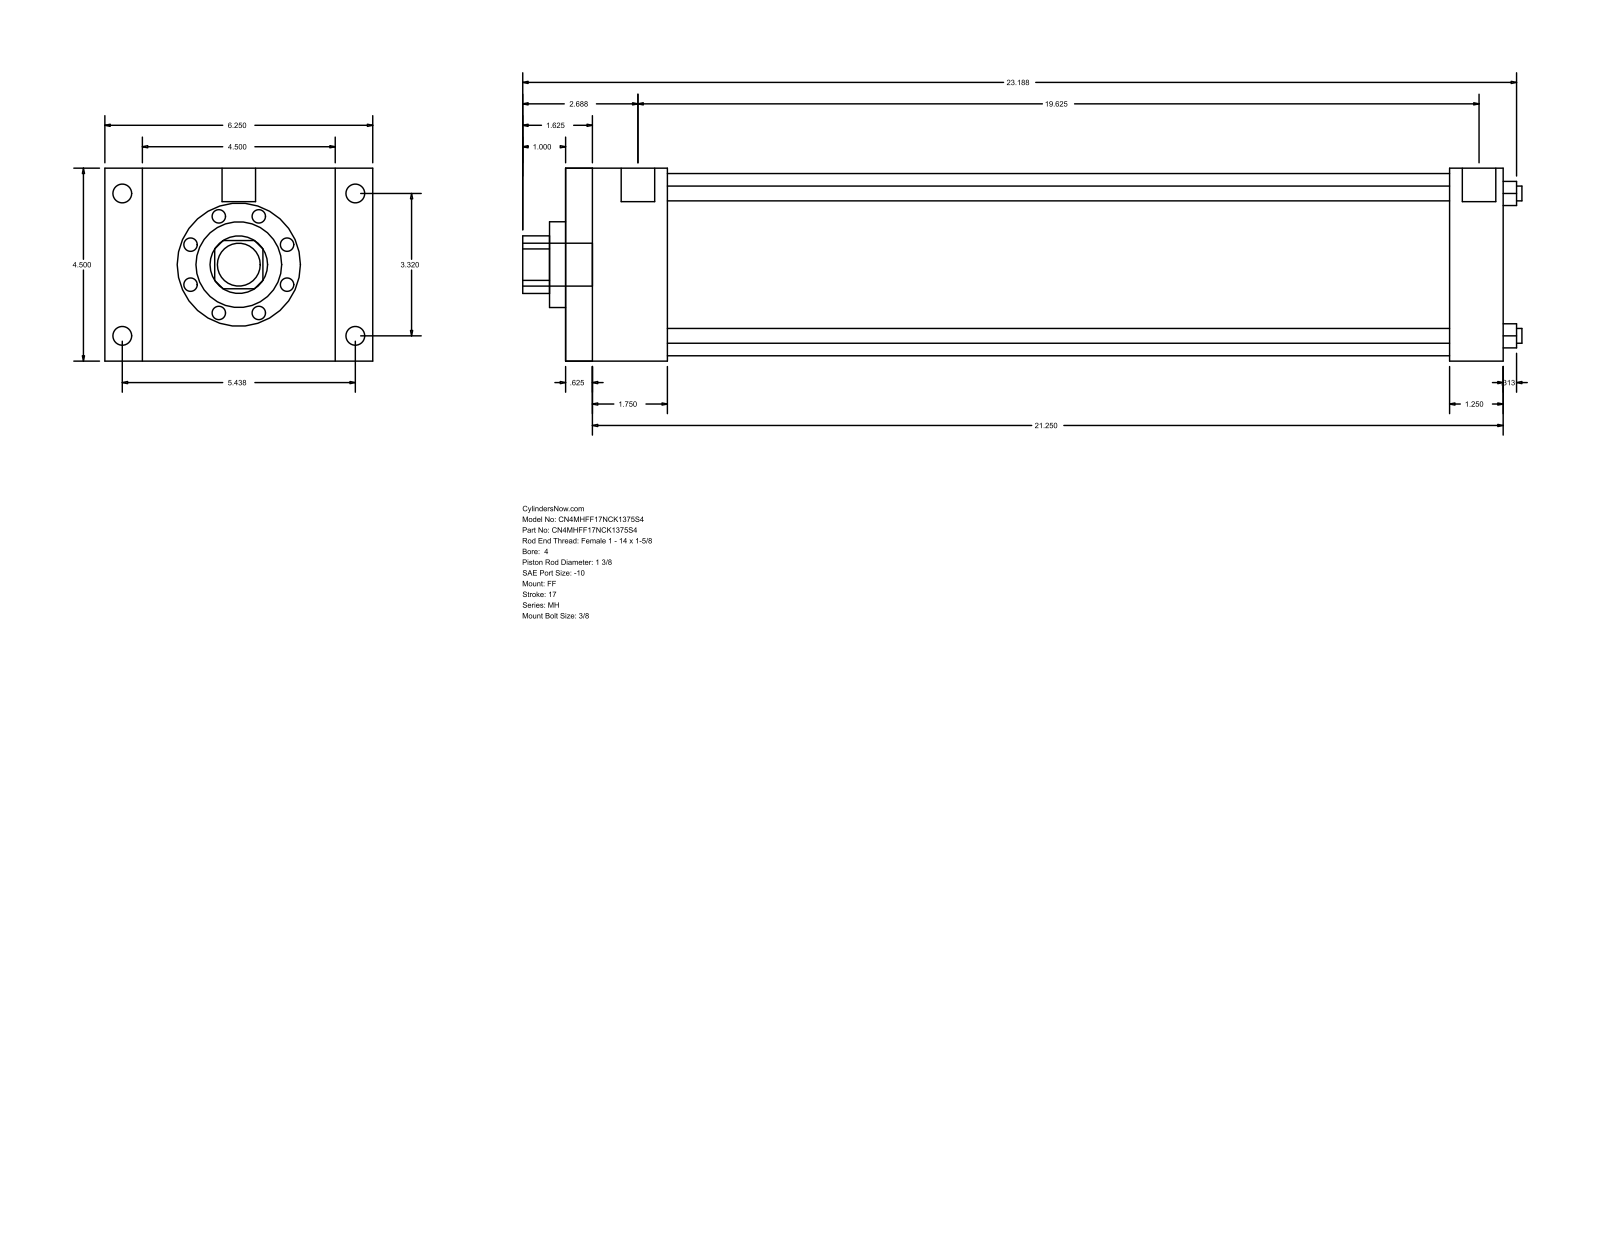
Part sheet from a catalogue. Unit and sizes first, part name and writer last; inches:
Units: inches
Overall size (bounding box): 23.313 × 6.25 × 4.5
Round holes (diameter × count): ⌀0.345 ×4, ⌀1.375 ×1, ⌀2 ×1, ⌀4.25 ×1
Round bosses / shafts (diameter × count): ⌀0.438 ×4, ⌀0.344 ×4, ⌀0.781 ×2, ⌀1 ×1
Partial cylindrical surfaces — rounded edges, fillets, slot ends (radius × count): R0.672 ×1
Main face-to-face distances: 4.5, 21.875, 0.625, 21.25, 2.375, 1.75, 19.5, 20.625, 20, 18.25
Hole centre spacings: 2.347, 3.32, 4.695
Bodies: 0 solids, 92 faces (64 planar, 28 cylindrical, 0 other)
Part name (STEP PRODUCT): MH_FF__0400_1.375
STEP written by: GSSL Pune (CONFIG_CONTROL_DESIGN)
